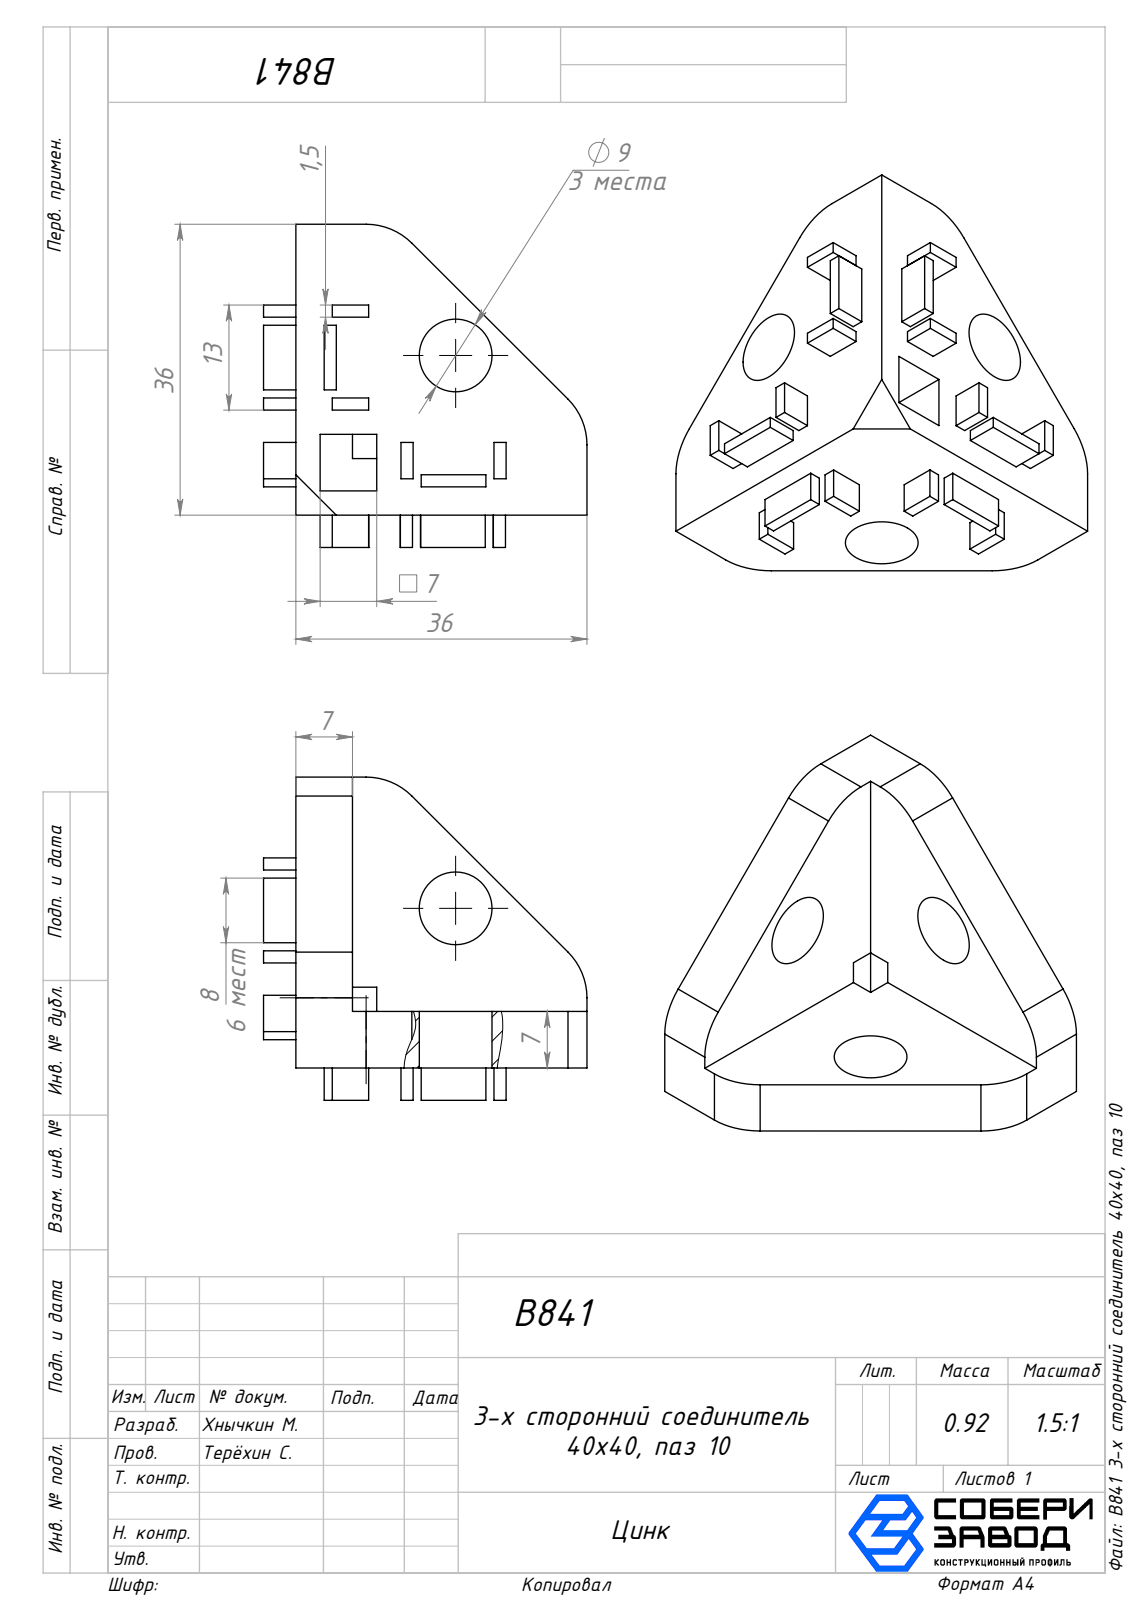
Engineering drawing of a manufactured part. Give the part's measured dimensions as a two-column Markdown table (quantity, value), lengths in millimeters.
| quantity | value |
| --- | --- |
| part name | B841 3-х сторонний соединитель 40х40, паз 10 |
| STEP written by | SolidWorks 2025 (AUTOMOTIVE_DESIGN) |
| units | millimeters |
| bodies | 1 solid, 120 faces (108 planar, 12 cylindrical, 0 other) |
| overall size | 47 × 40 × 40 |
| volume | 18 138 mm³ |
| surface area | 8 184 mm² |
| round holes (diameter × count) | 9 × 3 |
| partial cylindrical surfaces (radius × count) | 8 × 6 |
| main face-to-face distances | 7, 4, 1.5, 10, 3, 2, 11.5, 36, 4.5, 5.5 |
